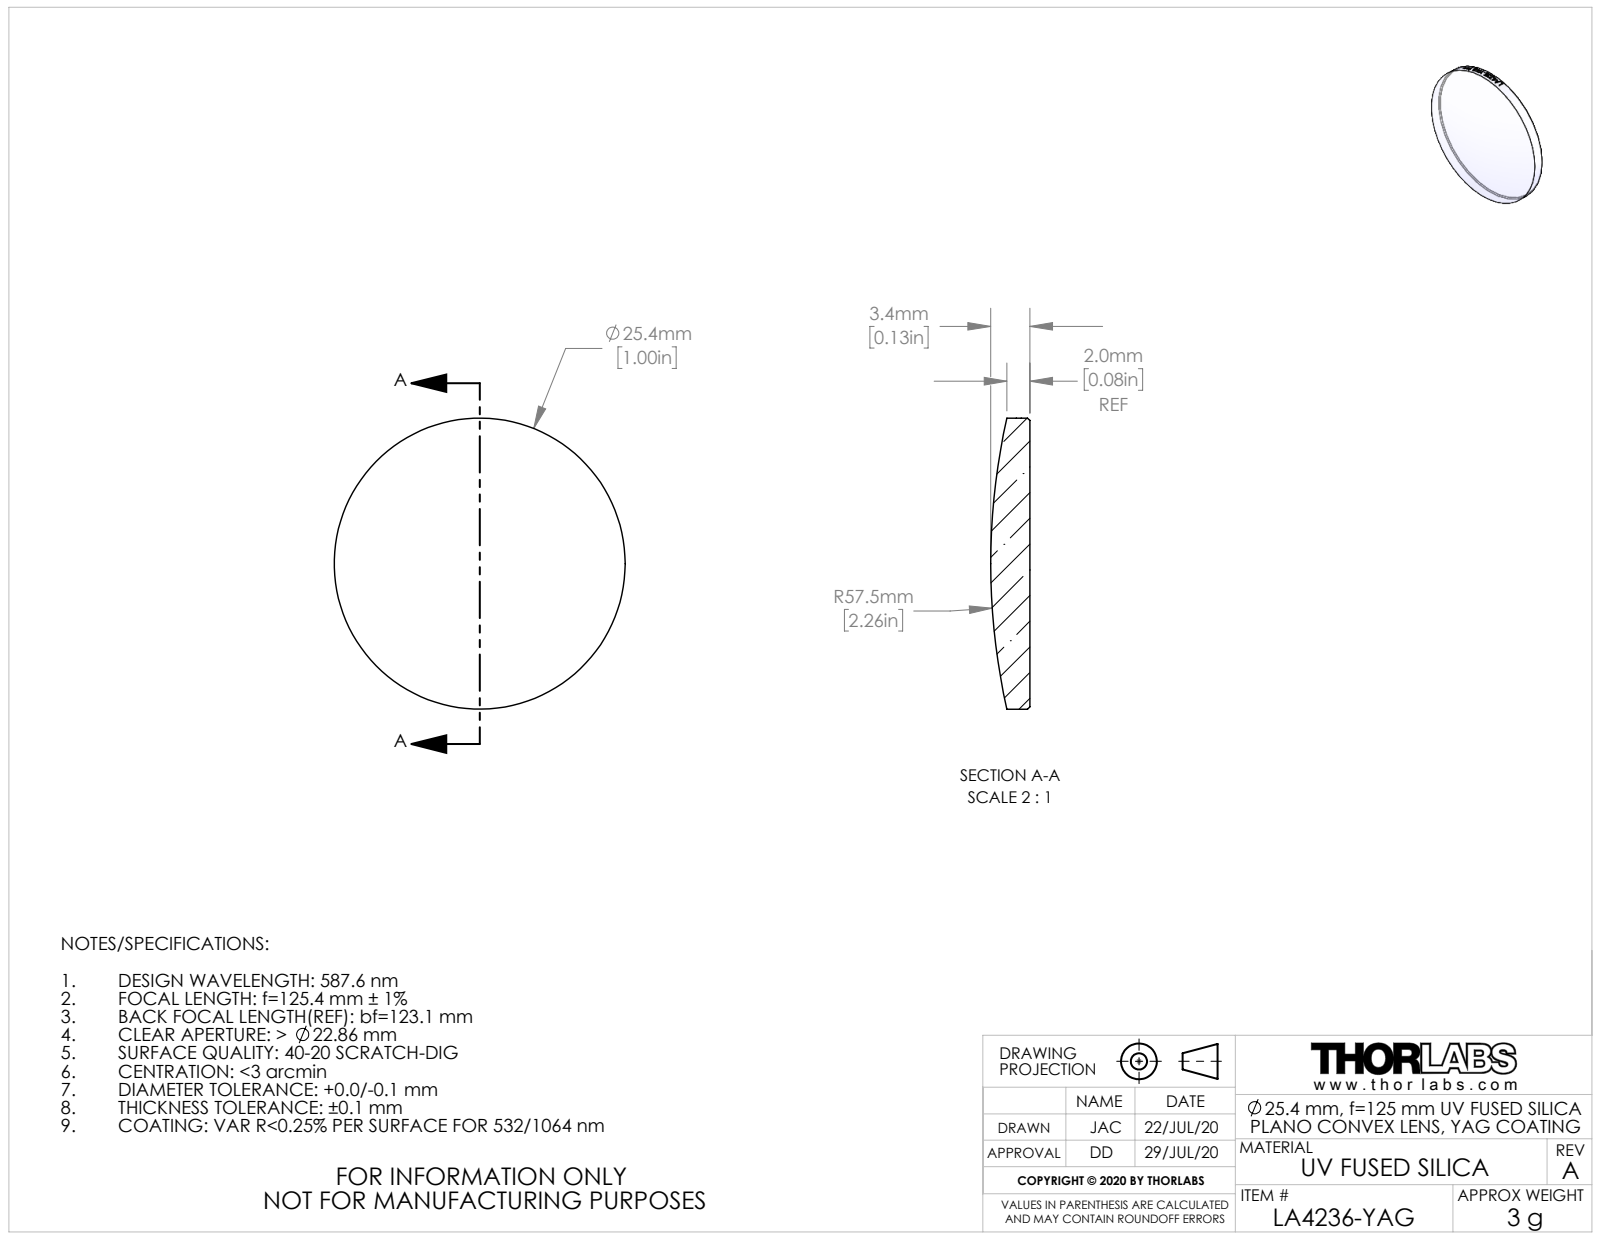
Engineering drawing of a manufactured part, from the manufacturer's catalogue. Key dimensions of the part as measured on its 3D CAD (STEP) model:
Part name (STEP PRODUCT): TTN217852-E0W
STEP written by: SolidWorks 2018 (CONFIG_CONTROL_DESIGN)
Units: millimetres
Bodies: 1 solid, 25 faces (1 planar, 20 cylindrical, 4 other)
Overall size (bounding box): 25.4 × 25.4 × 3.42
Volume: 1 373 mm³ · Surface area: 1 170 mm²
Round bosses / shafts (diameter × count): ⌀25.4 ×1
